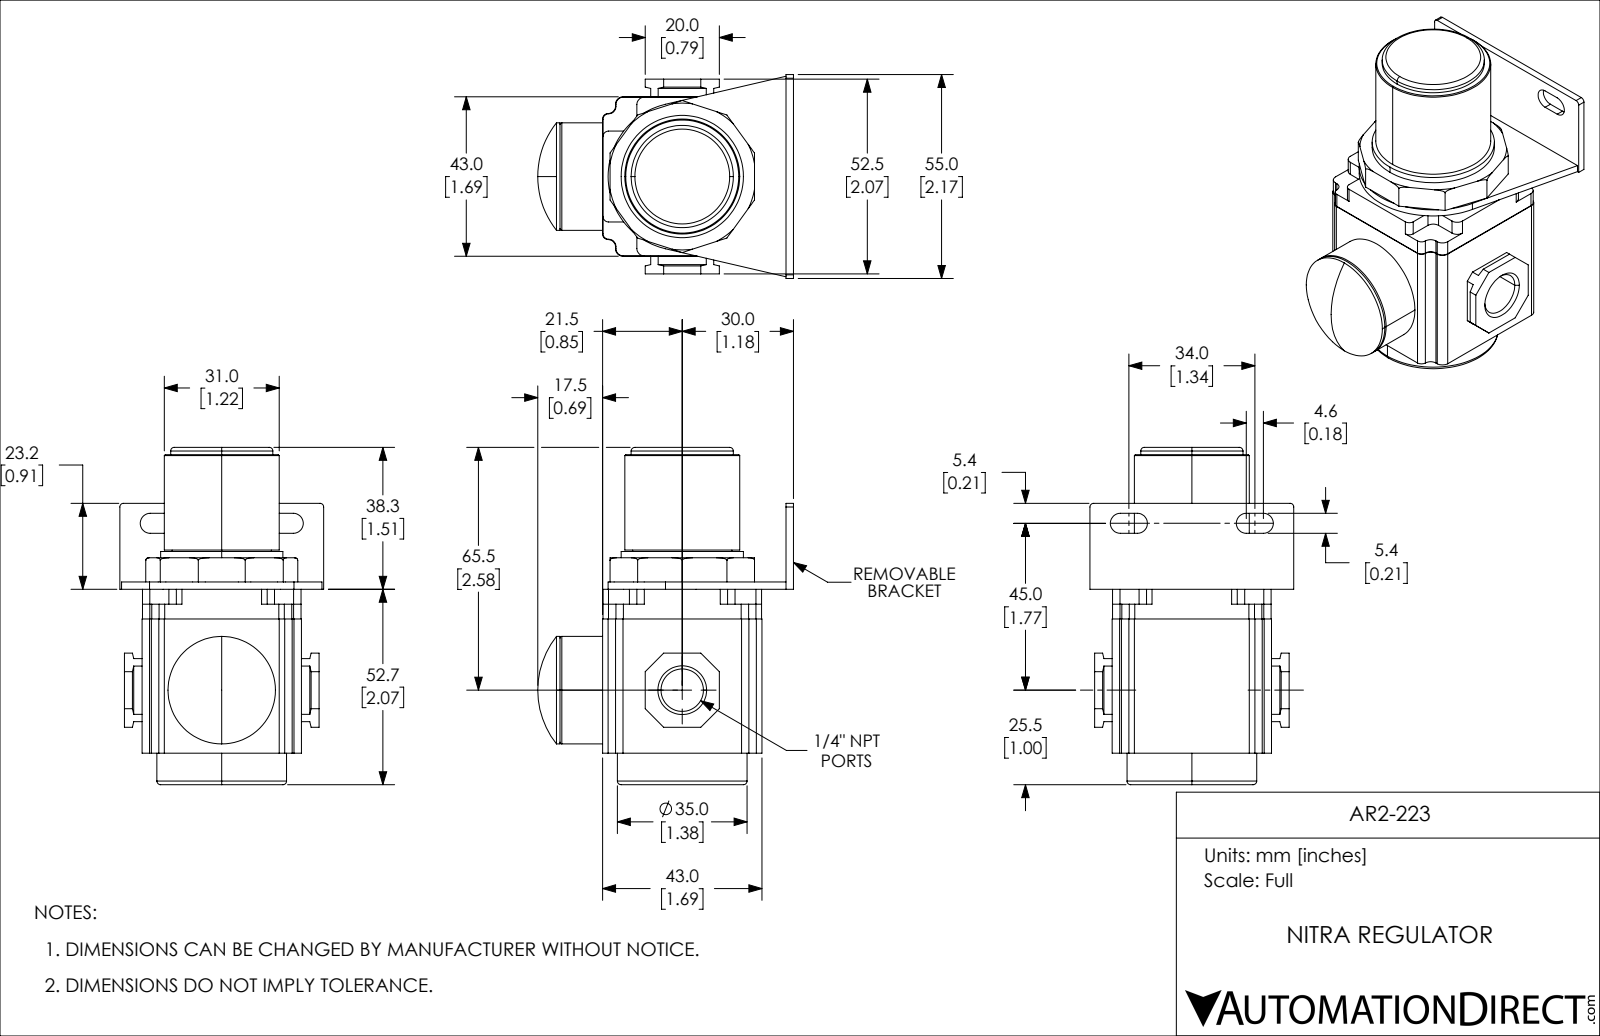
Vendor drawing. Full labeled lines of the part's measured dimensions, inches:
Part name (STEP PRODUCT): AR2-223
STEP written by: SolidWorks 2019 (CONFIG_CONTROL_DESIGN)
Units: inches
Bodies: 1 solid, 193 faces (108 planar, 61 cylindrical, 24 other)
Overall size (bounding box): 3.583 × 2.717 × 2.165
Volume: 8.089 in³ · Surface area: 35.42 in²
Round holes (diameter × count): ⌀0.451 ×1
Round bosses / shafts (diameter × count): ⌀1.378 ×1, ⌀1.299 ×1, ⌀1.22 ×1, ⌀1.142 ×1, ⌀1.086 ×1, ⌀1.054 ×1
Partial cylindrical surfaces — rounded edges, fillets, slot ends (radius × count): R0.079 ×24, R0.059 ×12, R0.106 ×4, R0.039 ×2, R0.787 ×1
Main face-to-face distances: 0.335, 0.079, 0.256, 1.693, 2.075, 1.74, 1.689, 2.154, 1.819, 1.429
